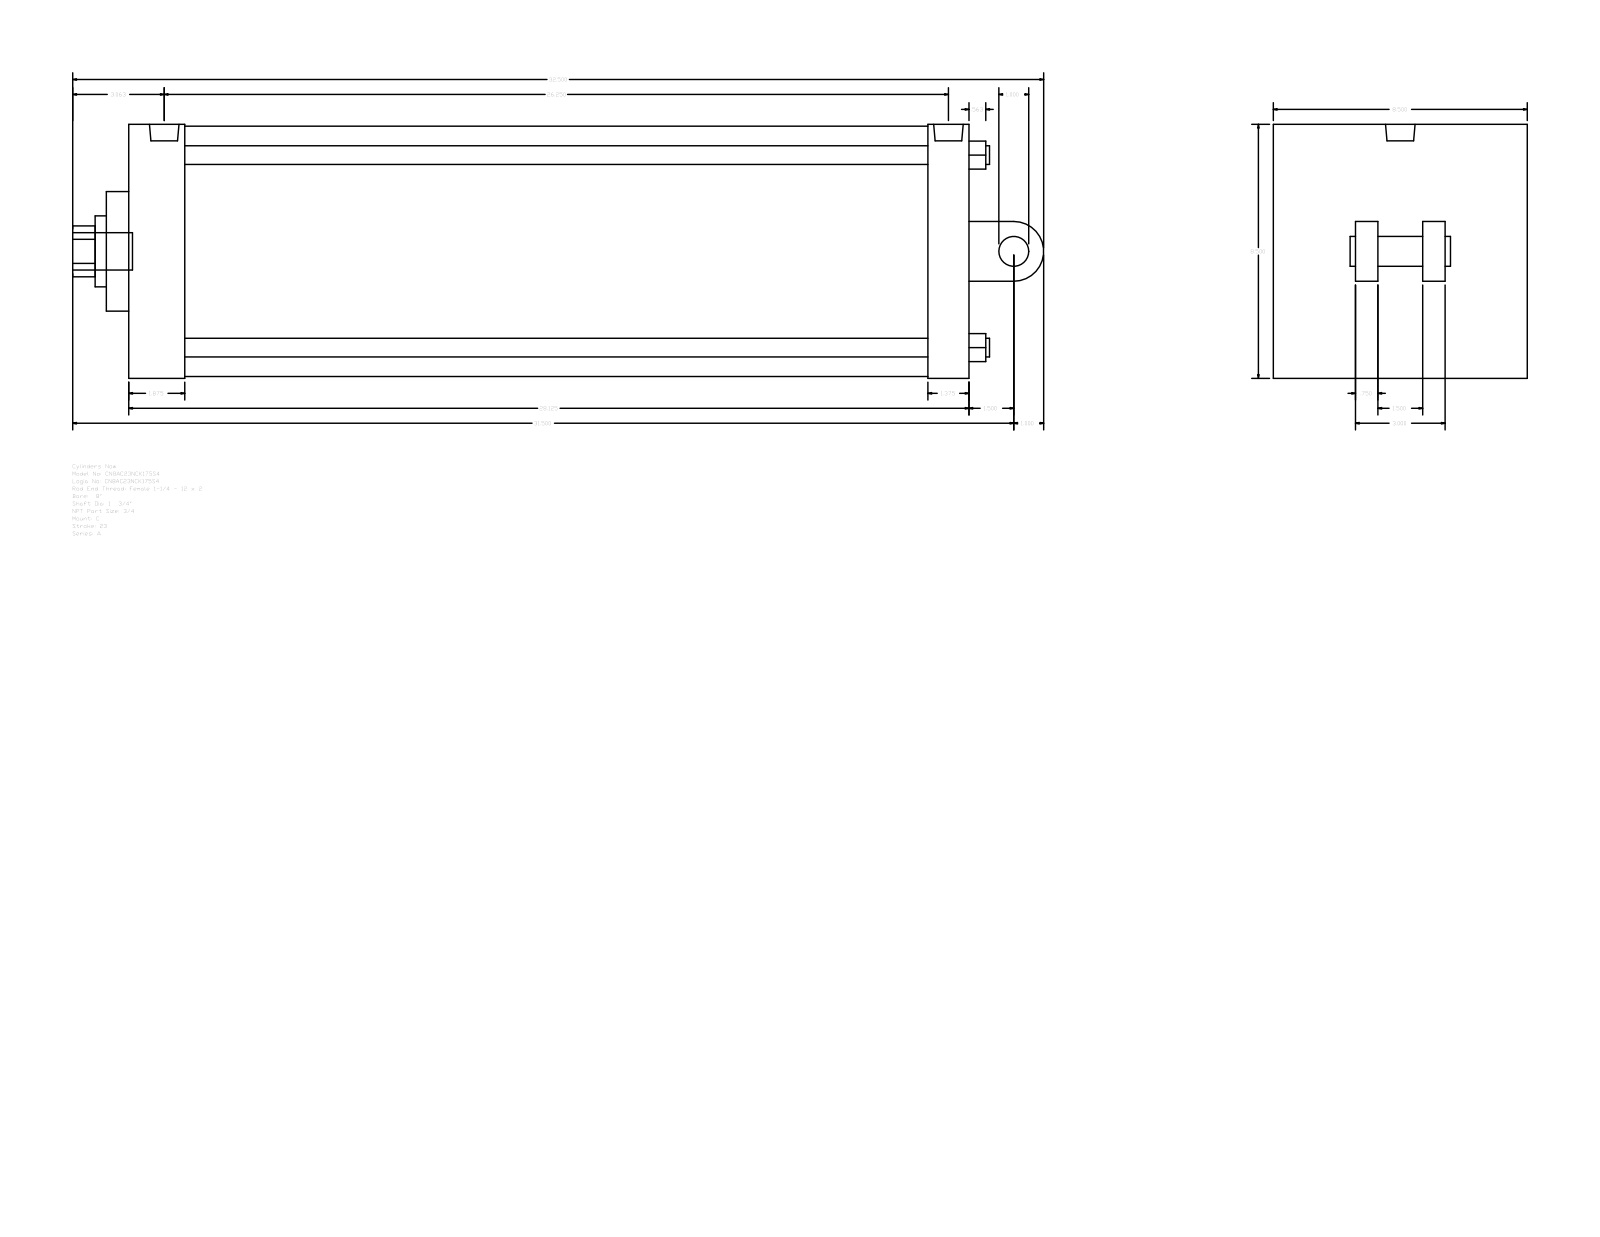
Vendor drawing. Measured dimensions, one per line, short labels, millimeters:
name: A_C__0800_1.75
written by: GSSL Pune (CONFIG_CONTROL_DESIGN)
unit: mm
bodies: 0 solids, 104 faces (75 planar, 29 cylindrical, 0 other)
size: 825.5 × 215.9 × 215.9
holes: 4× ⌀15.88, 2× ⌀15.08, 1× ⌀25.12, 1× ⌀44.45, 1× ⌀60.33, 1× ⌀212.72
bosses: 2× ⌀15.08, 1× ⌀31.75, 1× ⌀25.4, 1× ⌀25.12
rounds: 1× R21.63, 1× R25.4
face distances: 714.38, 215.9, 19.05, 57.15, 34.92, 47.63, 666.75, 679.46, 631.83, 88.9
hole spacings: 115.67, 163.58, 231.34, 6.35
